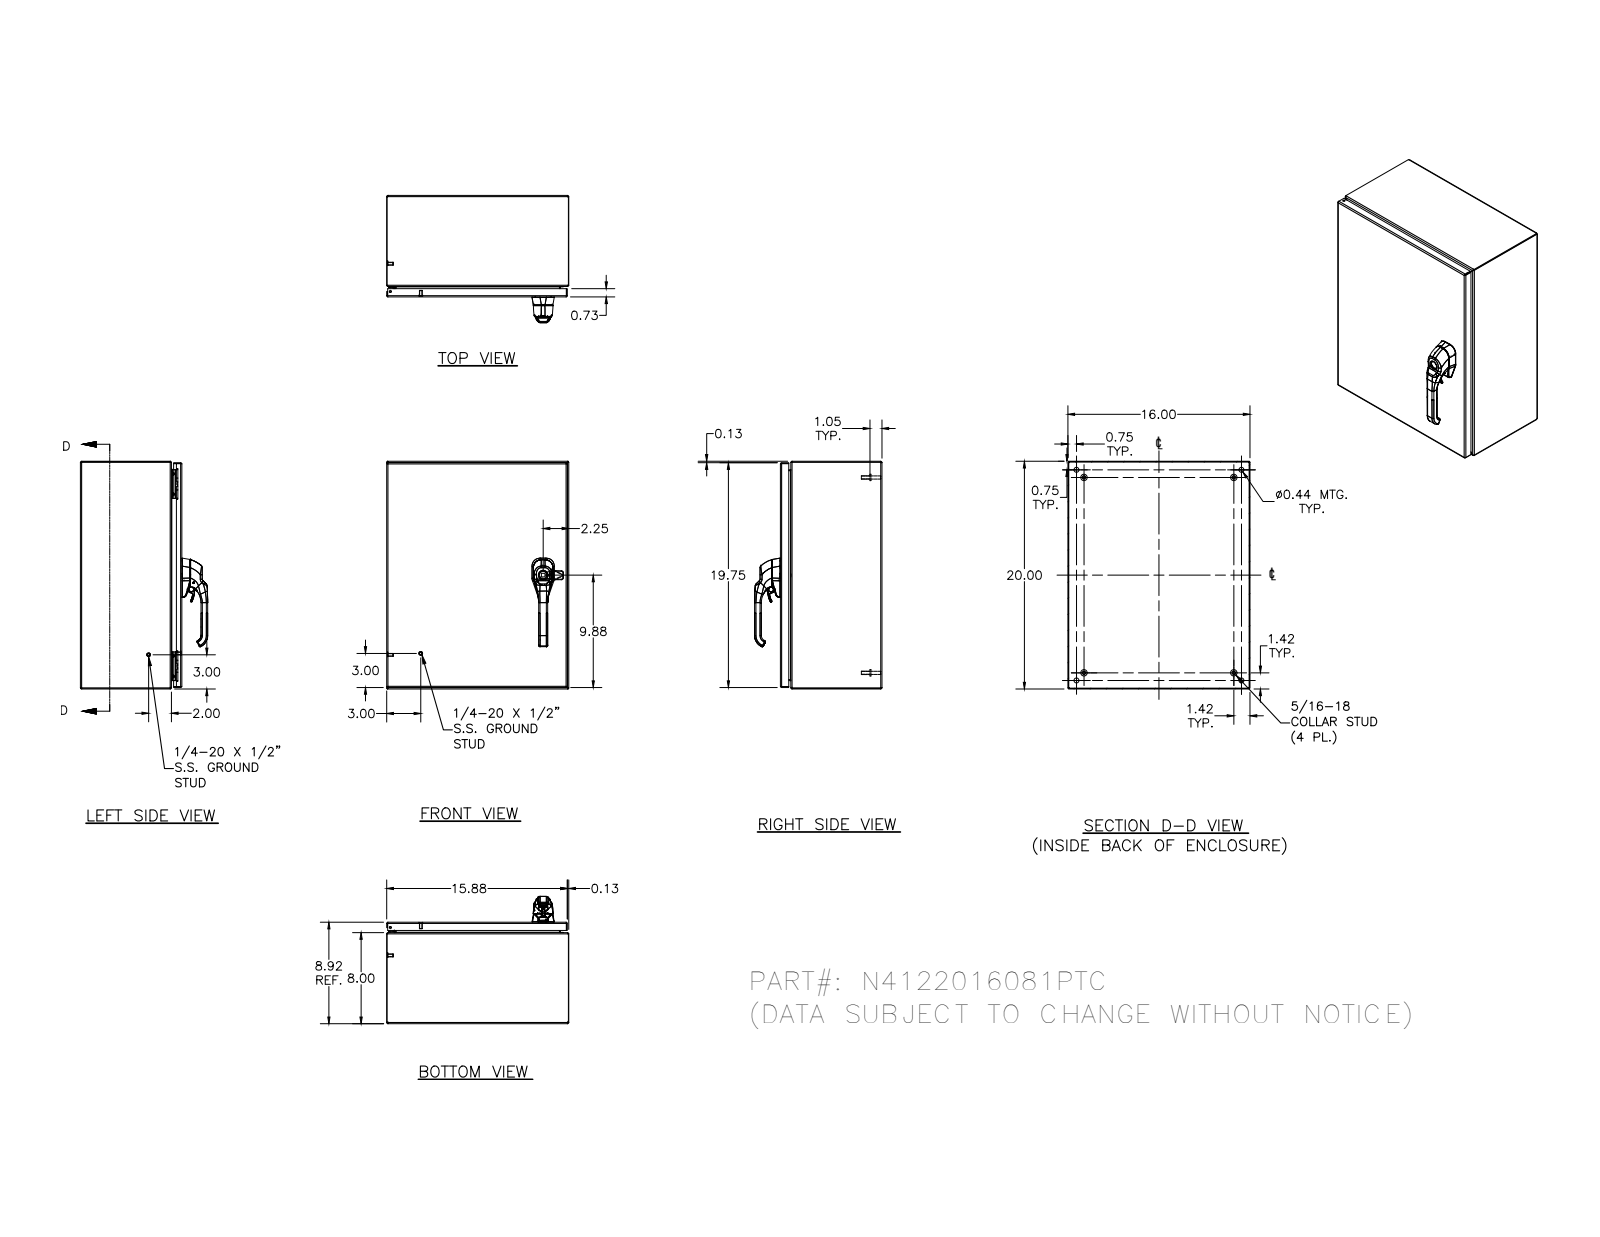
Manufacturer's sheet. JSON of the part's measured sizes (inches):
{"part_name": "N4122016081PTC", "step_written_by": "SolidWorks 2018 (AUTOMOTIVE_DESIGN)", "units": "inches", "bodies": {"solids": 28, "faces": 1280, "planar": 417, "cylindrical": 474, "other": 389}, "overall_size": [20, 16, 11.095], "volume_in3": 110.4, "surface_area_in2": 2777, "round_holes": [[0.188, 5], [0.093, 4], [0.152, 4], [0.167, 4], [0.172, 4], [0.437, 4], [0.28, 3], [0.156, 2], [0.187, 1]], "round_bosses_or_shafts": [[0.25, 10], [0.563, 4], [0.36, 4], [0.32, 4], [0.3, 4], [0.275, 4], [0.256, 4], [0.164, 4]], "partial_cylinders_radius": [[0.031, 30], [0.05, 26], [0.105, 20], [0.016, 18], [0.125, 14], [0.032, 8], [0.067, 8], [0.068, 8]], "face_to_face_distances": [0.074, 8.843, 8.917, 15.926, 8.769, 19.926, 16, 15.852, 20, 19.852], "hole_center_spacings": [15.996, 0.017, 0.66, 16.004, 16.656, 0.019, 0.5, 0.648]}
